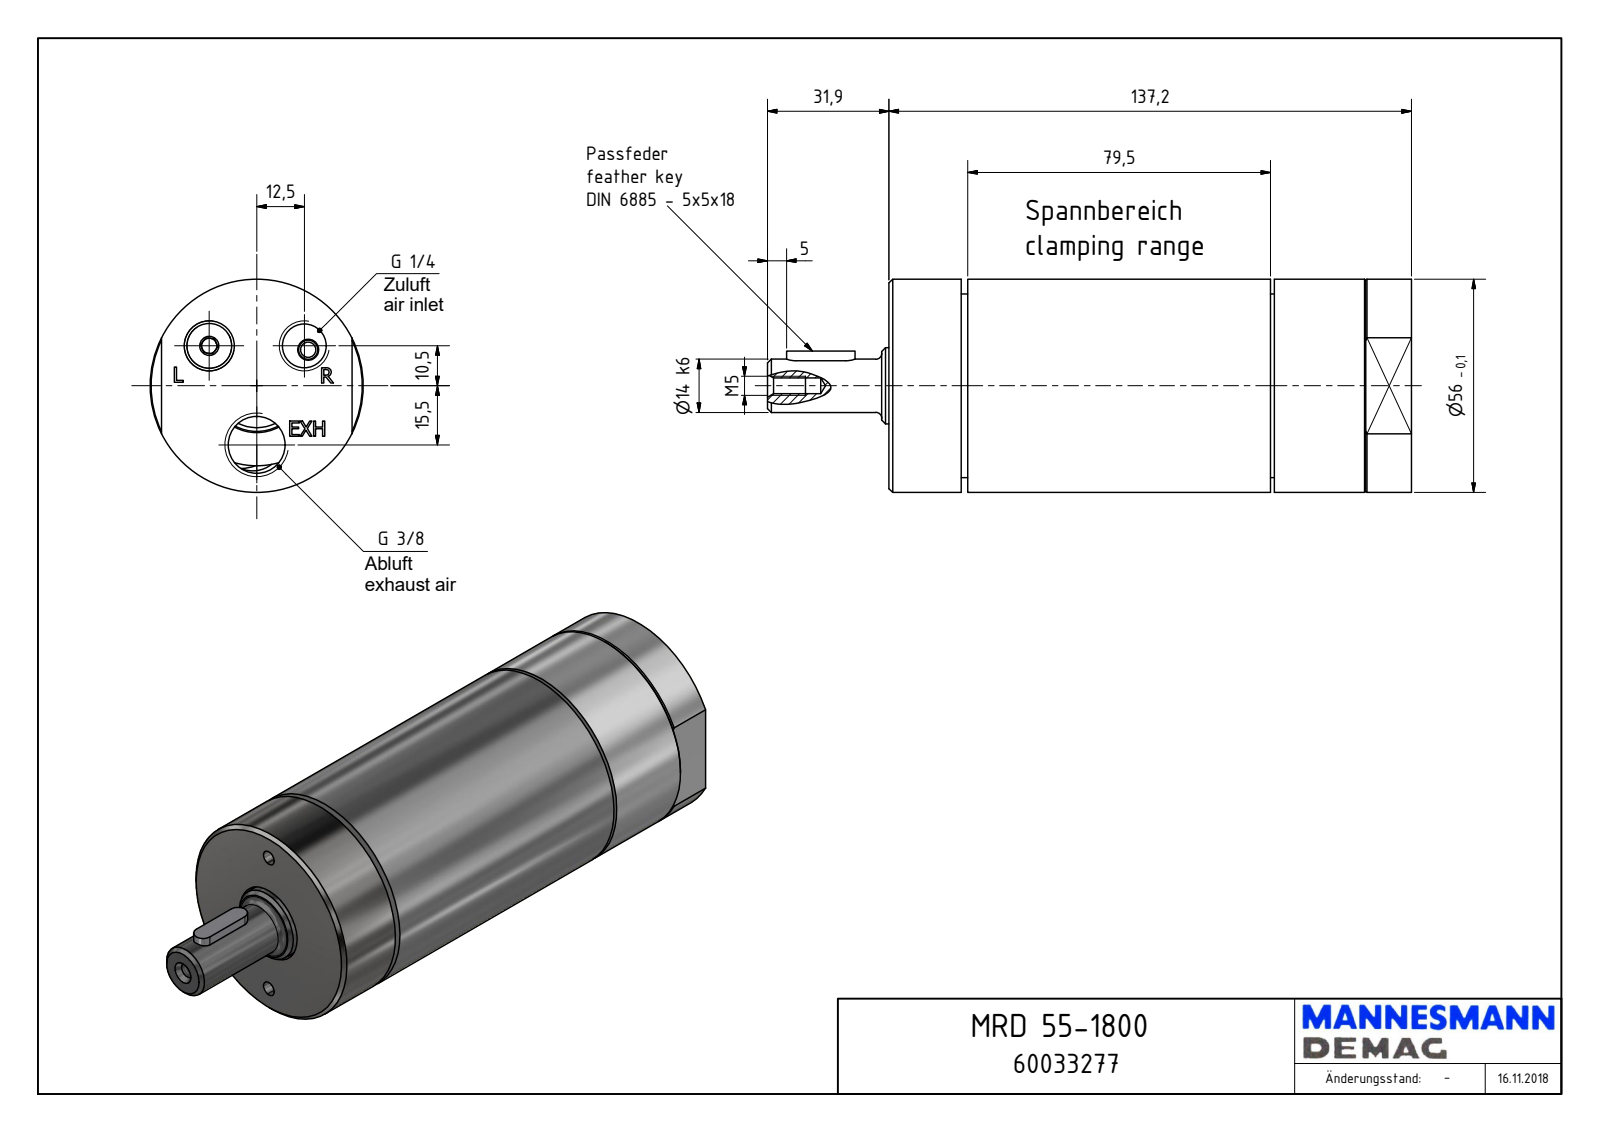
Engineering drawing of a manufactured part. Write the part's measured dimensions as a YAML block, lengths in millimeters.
part_name: "MRD 55-1800_60033277"
step_written_by: "Autodesk Inventor 2018 (AUTOMOTIVE_DESIGN)"
units: millimeters
bodies: {solids: 1, faces: 183, planar: 105, cylindrical: 32, other: 46}
overall_size: [169.1, 56, 56]
volume: 336454
surface_area: 37202
round_holes:
  - {diameter: 4, count: 3}
  - {diameter: 4.13, count: 1}
  - {diameter: 11.45, count: 1}
  - {diameter: 14.95, count: 1}
  - {diameter: 21, count: 1}
  - {diameter: 21.25, count: 1}
  - {diameter: 23.54, count: 1}
  - {diameter: 26, count: 1}
  - {diameter: 48.38, count: 1}
round_bosses_or_shafts:
  - {diameter: 56, count: 1}
  - {diameter: 48.18, count: 1}
  - {diameter: 19.95, count: 1}
  - {diameter: 14, count: 1}
partial_cylinders:
  - {radius: 2.5, count: 2}
  - {radius: 6, count: 2}
  - {radius: 5.72, count: 1}
  - {radius: 20.26, count: 1}
  - {radius: 23, count: 1}
face_to_face_distances: [137.2, 20.7, 116.5, 100.2, 79.5, 37, 101.2, 19, 1.7, 81.2]
hole_center_spacings: [16.32, 21, 28.85, 33.89, 5.5, 15.5, 25, 36.5]
